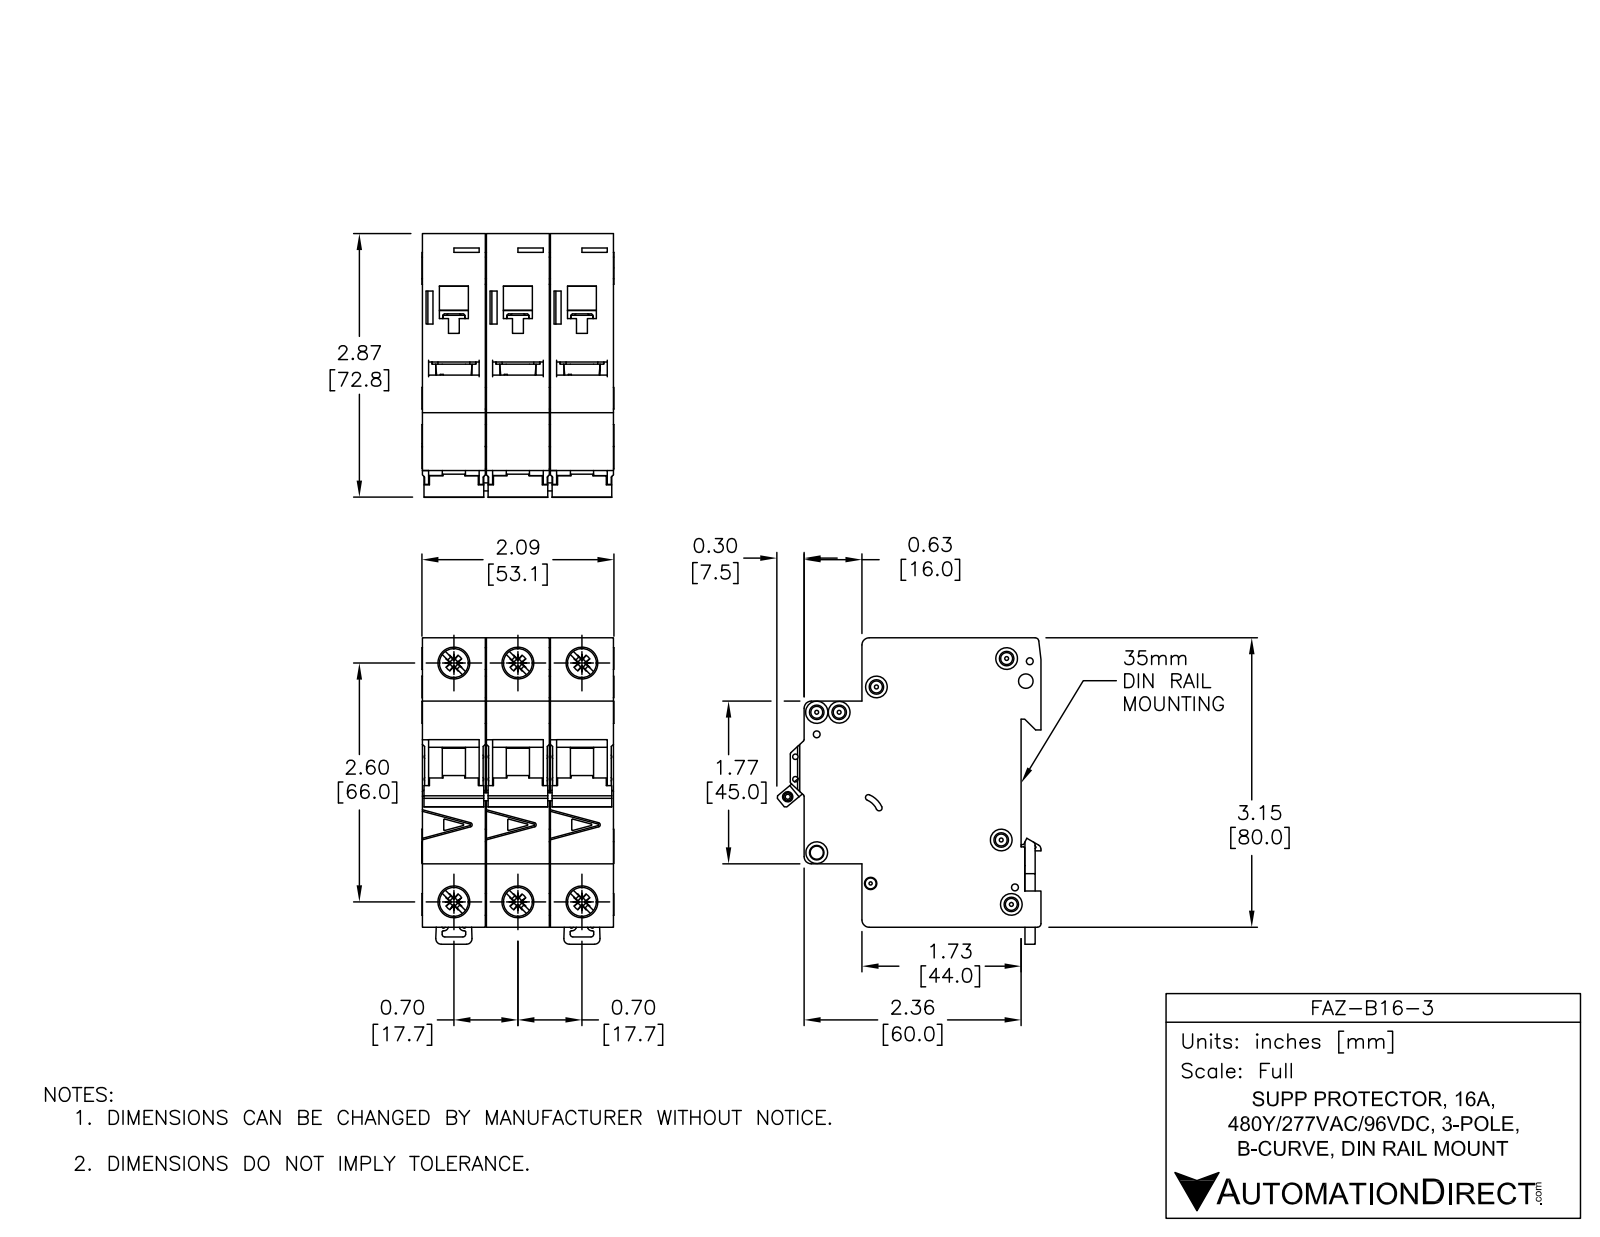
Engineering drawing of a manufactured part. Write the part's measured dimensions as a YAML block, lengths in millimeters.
part_name: "FAZ-B16-3"
step_written_by: "SolidWorks 2014 (AUTOMOTIVE_DESIGN)"
units: millimeters
bodies: {solids: 11, faces: 1650, planar: 697, cylindrical: 590, other: 363}
overall_size: [84.78, 73.04, 53.1]
volume: 224680
surface_area: 58052
round_holes:
  - {diameter: 3.6, count: 6}
  - {diameter: 8.2, count: 4}
  - {diameter: 1.9, count: 3}
  - {diameter: 1.09, count: 2}
  - {diameter: 1.5, count: 2}
  - {diameter: 4, count: 2}
  - {diameter: 7.15, count: 2}
  - {diameter: 2.15, count: 1}
  - {diameter: 2.2, count: 1}
  - {diameter: 2.55, count: 1}
  - {diameter: 3.3, count: 1}
  - {diameter: 3.4, count: 1}
round_bosses_or_shafts:
  - {diameter: 6, count: 4}
  - {diameter: 2.5, count: 3}
  - {diameter: 8.2, count: 2}
partial_cylinders:
  - {radius: 0.25, count: 68}
  - {radius: 0.5, count: 25}
  - {radius: 1, count: 12}
  - {radius: 2, count: 12}
  - {radius: 0.2, count: 11}
  - {radius: 1.8, count: 3}
  - {radius: 0.8, count: 2}
  - {radius: 3, count: 2}
face_to_face_distances: [17.7, 17.5, 35.4, 35.2, 52.9, 17.9, 79.48, 5.5, 49.5, 44]
hole_center_spacings: [17.7, 68.33, 66, 6.2, 13.64, 35.4, 74.89, 4.81]
